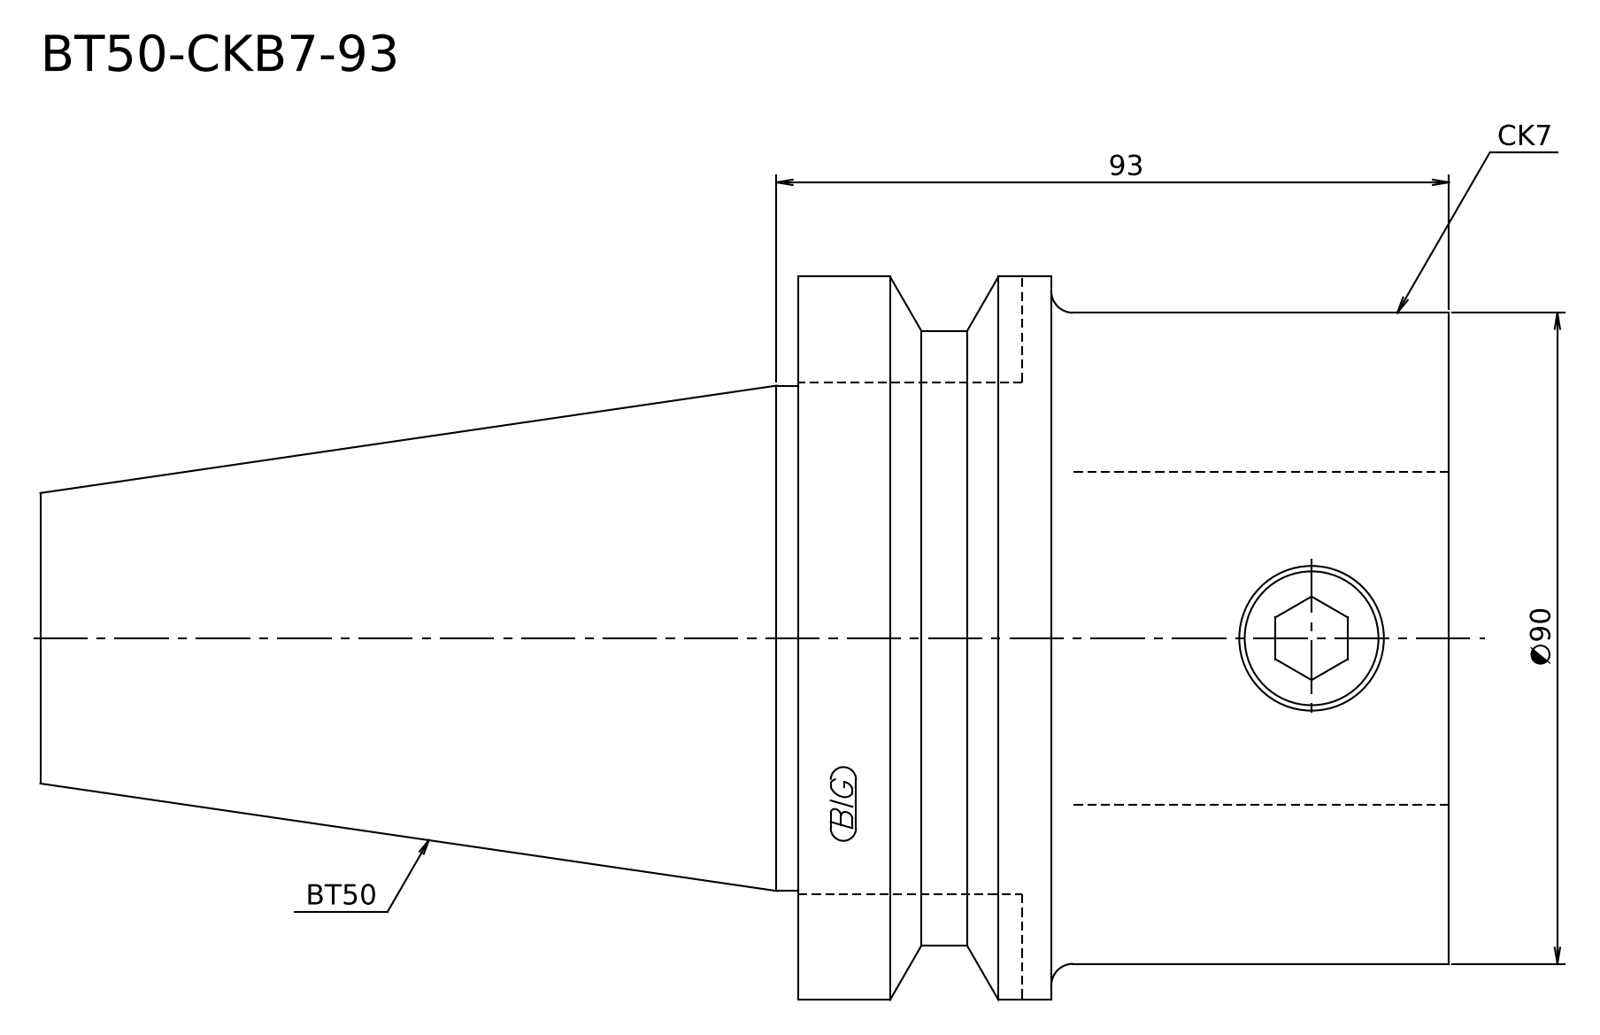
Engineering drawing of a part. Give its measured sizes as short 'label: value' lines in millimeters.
written by: Kubotek KeyCreator V8.5.1 (14335) (CONFIG_CONTROL_DESIGN)
unit: mm
bodies: 1 solid, 13 faces (4 planar, 5 cylindrical, 4 other)
size: 194.8 × 100 × 100
volume: 861 841 mm³; area: 59 653 mm²
bosses: 1× ⌀100, 1× ⌀90, 1× ⌀85, 1× ⌀69.85
face distances: 90, 194.8, 104.8, 55, 35, 139.8
